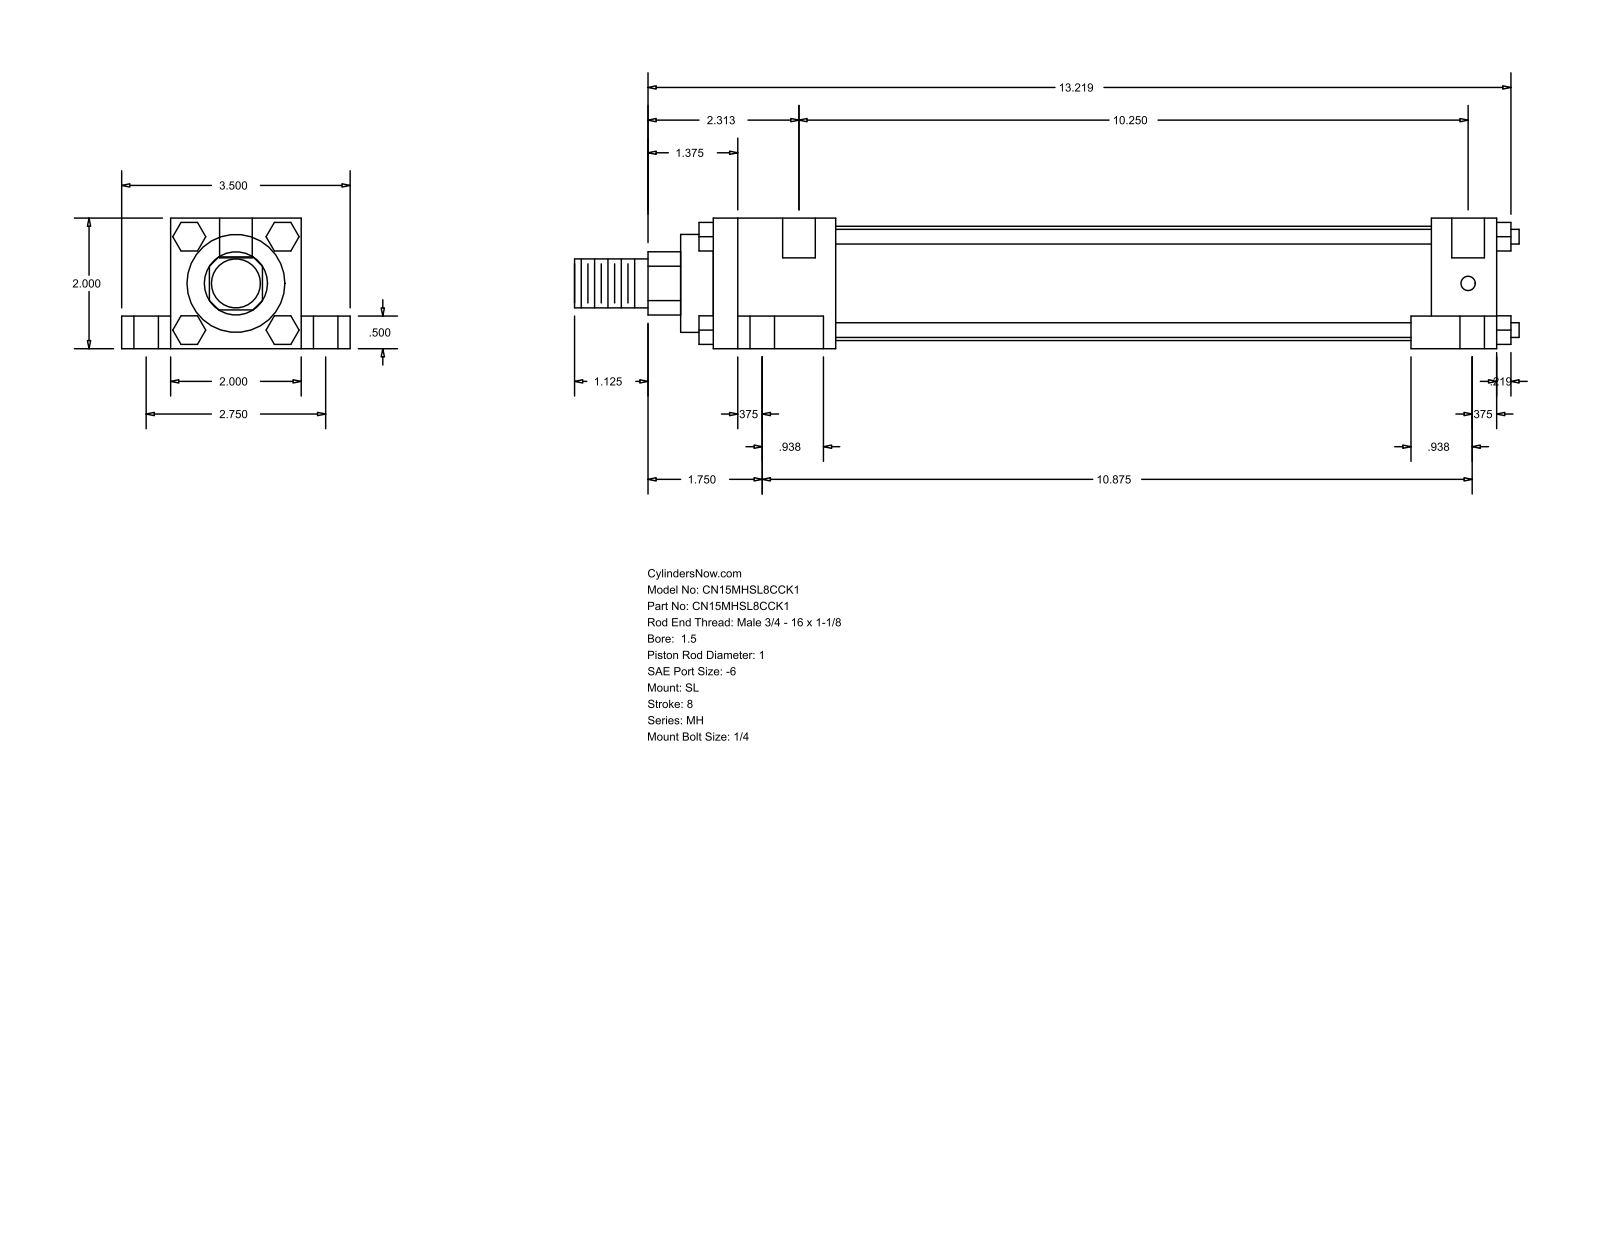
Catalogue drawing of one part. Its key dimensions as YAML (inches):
part_name: "MH_SL__0150_1"
step_written_by: "GSSL Pune (CONFIG_CONTROL_DESIGN)"
units: inches
bodies: {solids: 0, faces: 148, planar: 112, cylindrical: 36, other: 0}
overall_size: [14.469, 3.5, 2]
round_holes:
  - {diameter: 0.219, count: 4}
  - {diameter: 0.375, count: 4}
  - {diameter: 0.625, count: 4}
  - {diameter: 0.5, count: 2}
round_bosses_or_shafts:
  - {diameter: 0.225, count: 4}
  - {diameter: 1.75, count: 1}
  - {diameter: 1.5, count: 1}
  - {diameter: 1, count: 1}
  - {diameter: 0.75, count: 1}
partial_cylinders:
  - {radius: 0.484, count: 1}
face_to_face_distances: [2, 0.5, 1.5, 0.75, 2.75, 12, 1, 0.375, 1.313, 10.313]
hole_center_spacings: [1.376, 1.443, 1.485, 2.75, 10.375, 10.404, 10.528, 10.875]
